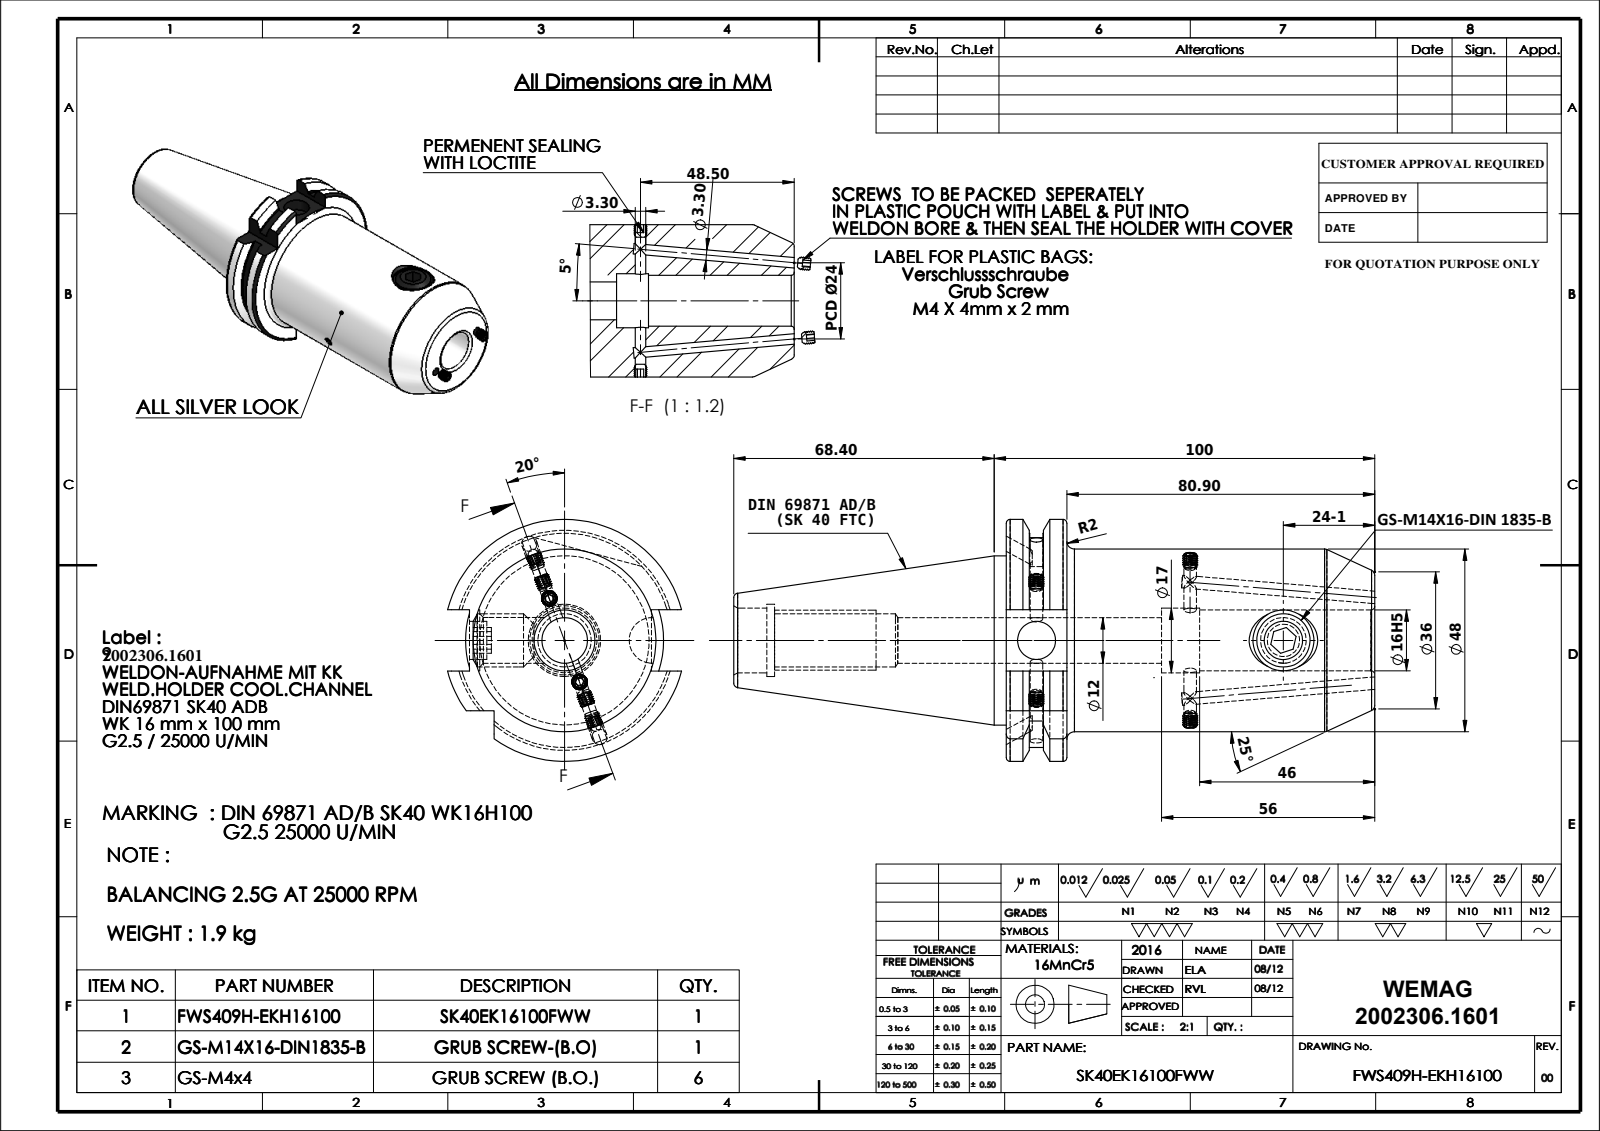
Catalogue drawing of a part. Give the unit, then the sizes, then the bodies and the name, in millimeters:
Units: millimetres
Overall size (bounding box): 174.92 × 63.55 × 61.48
Round holes (diameter × count): ⌀3.3 ×5, ⌀12 ×2, ⌀16 ×2, ⌀10 ×1, ⌀14 ×1, ⌀17 ×1, ⌀19 ×1
Round bosses / shafts (diameter × count): ⌀4 ×6, ⌀48 ×1, ⌀44.45 ×1, ⌀14 ×1
Partial cylindrical surfaces — rounded edges, fillets, slot ends (radius × count): R28.12 ×1, R31.77 ×1
Main face-to-face distances: 15.9, 96.8, 80.9, 16.1, 47.8, 71.6, 87.5, 168.4, 10.7, 60.9
Hole centre spacings: 40.4, 64.85
Volume: 225 627 mm³ · Surface area: 39 550 mm²
Bodies: 8 solids, 431 faces (99 planar, 116 cylindrical, 216 other)
Part name (STEP PRODUCT): 91406-WK216100; SK40EK16100FWW; GS-M14X16-DIN1835-B_ISO 4026 - M12 x 12-N; GS-M4X4_DIN 913 - M4 x 10-N
STEP written by: SolidWorks 2009 (CONFIG_CONTROL_DESIGN)
